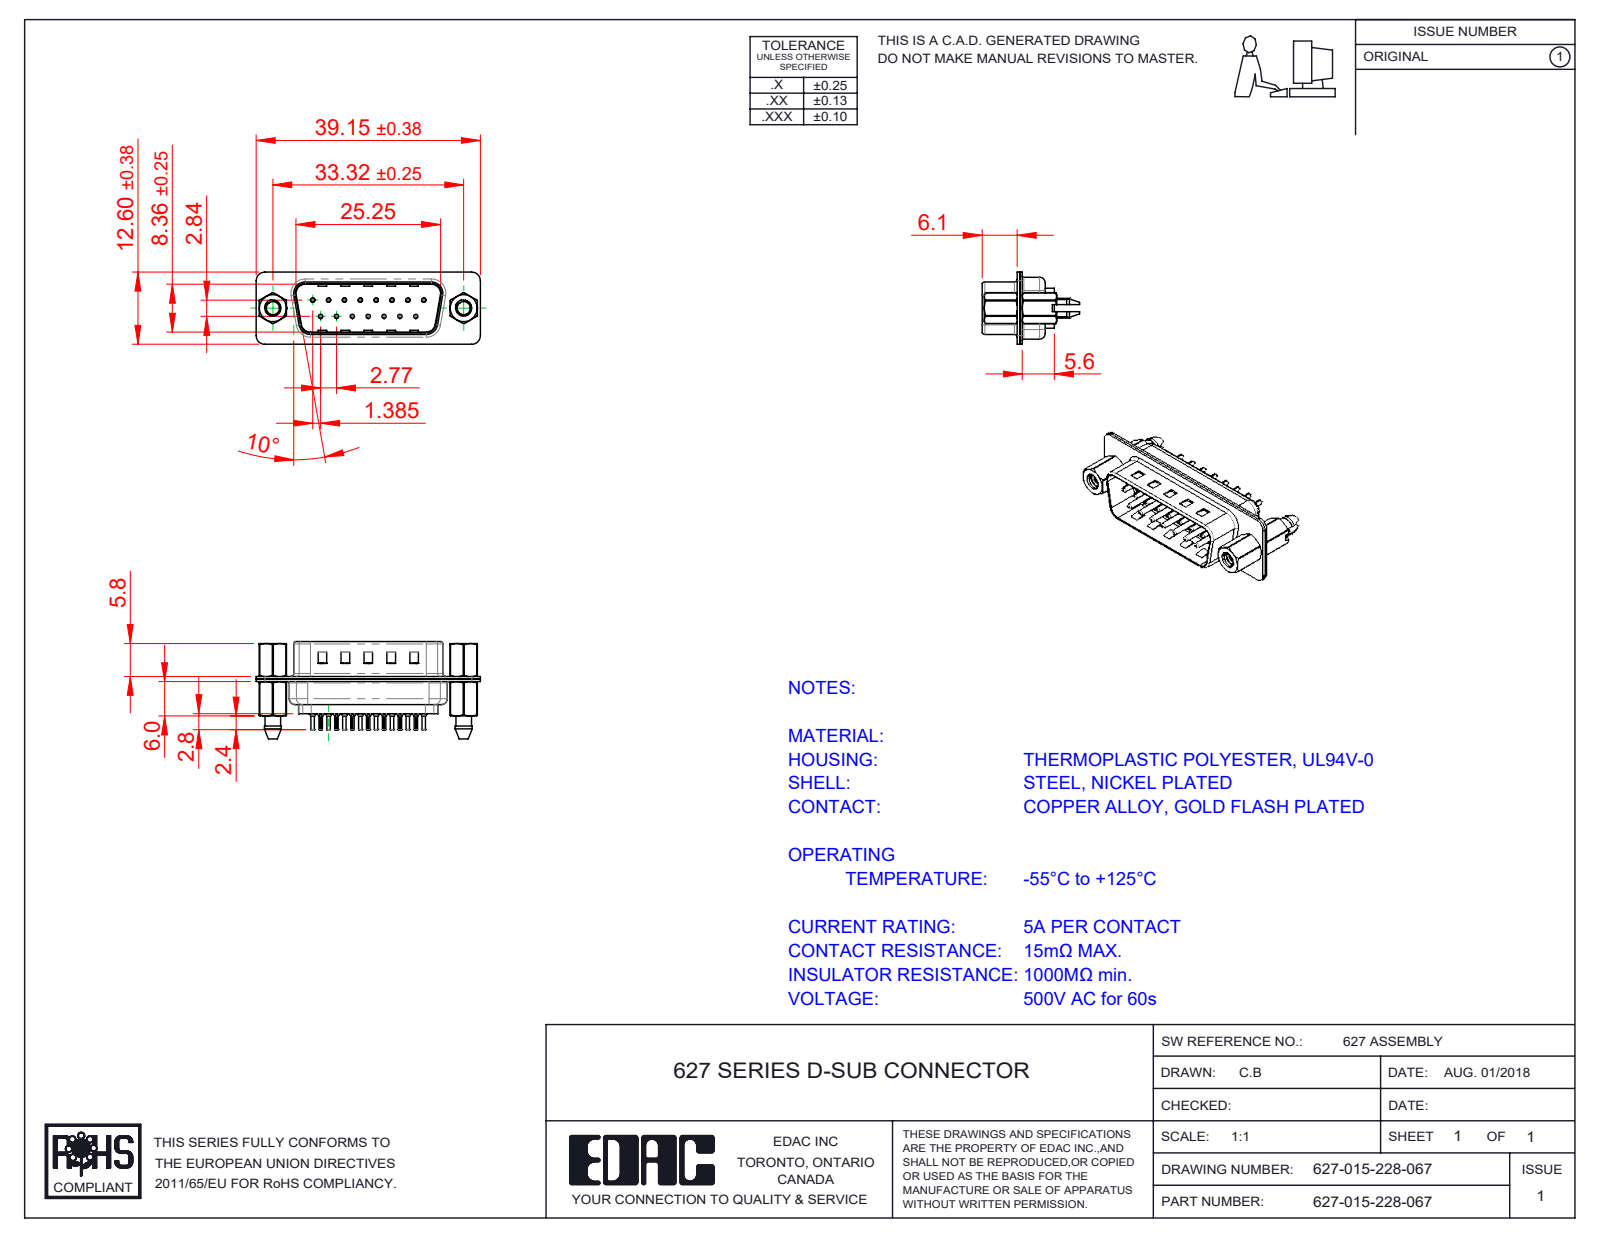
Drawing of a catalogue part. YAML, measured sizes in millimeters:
part_name: "627 Shell Rear_15 Contacts; 627 4-40 Threaded Boardlock_FF; 627 4-40 Hex Standoff; 627 Shell Front_15 Contacts (+4 more)"
step_written_by: "SolidWorks 2020 (CONFIG_CONTROL_DESIGN)"
units: millimeters
bodies: {solids: 23, faces: 2133, planar: 559, cylindrical: 861, other: 713}
overall_size: [39.15, 19.4, 12.6]
volume: 2604
surface_area: 7048
round_holes:
  - {diameter: 0.2, count: 15}
  - {diameter: 0.35, count: 15}
  - {diameter: 1.1, count: 15}
  - {diameter: 1.6, count: 15}
  - {diameter: 2.26, count: 2}
  - {diameter: 2.29, count: 2}
  - {diameter: 4, count: 2}
  - {diameter: 4.8, count: 2}
round_bosses_or_shafts:
  - {diameter: 2, count: 15}
  - {diameter: 1.5, count: 15}
  - {diameter: 0.75, count: 15}
  - {diameter: 0.6, count: 15}
  - {diameter: 4.9, count: 2}
  - {diameter: 2.79, count: 2}
partial_cylinders:
  - {radius: 0.1, count: 30}
  - {radius: 1.5, count: 18}
  - {radius: 2, count: 12}
  - {radius: 1.6, count: 10}
  - {radius: 0.5, count: 8}
  - {radius: 0.25, count: 4}
  - {radius: 0.6, count: 4}
  - {radius: 0.65, count: 4}
face_to_face_distances: [0.4, 0.45, 6.05, 0.9, 0.82, 9.58, 6.5, 8.4, 4.76, 1.5]
hole_center_spacings: [3.16, 2.77, 5.54, 8.31, 11.08, 5.03, 5.04, 7.48]
